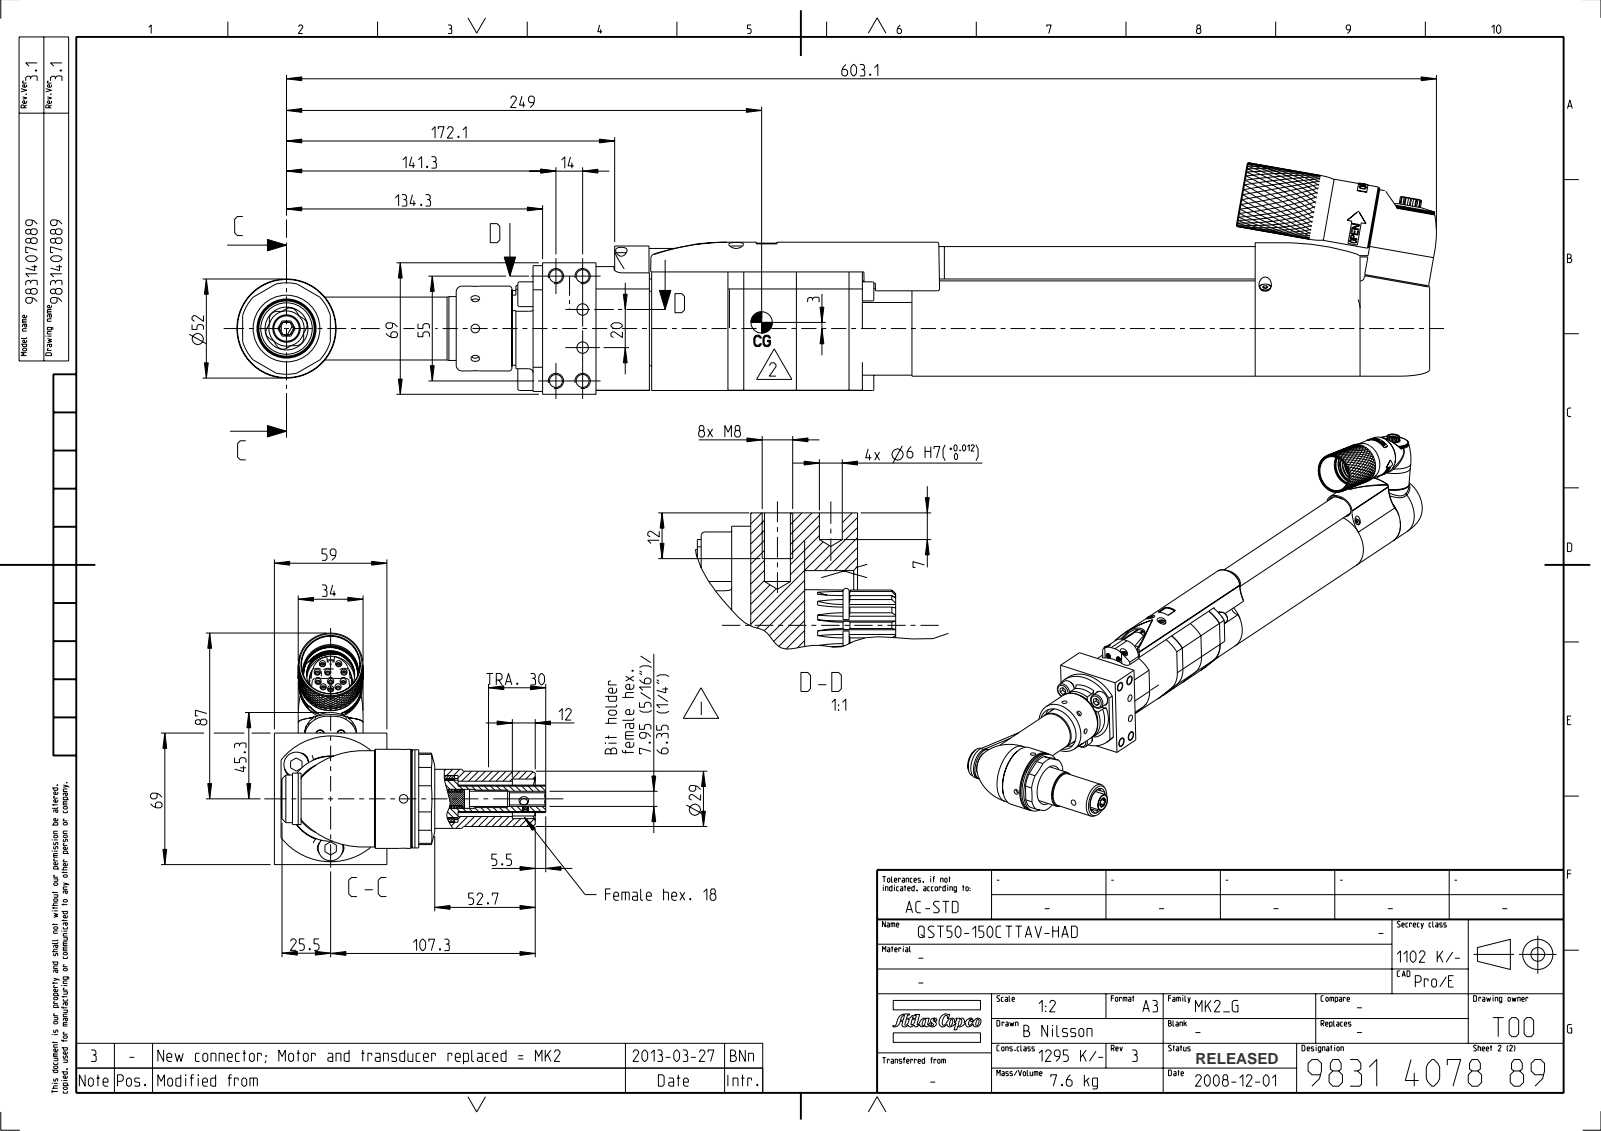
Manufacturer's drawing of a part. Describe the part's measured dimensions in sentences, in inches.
The part is named "4230260202; 4230260212_ASM; 4230265900; 0219110017 (+8 more)". Its 3-D file was written by "PRO/ENGINEER BY PARAMETRIC TECHNOLOGY CORPORATION, 2012420 (CONFIG_CONTROL_DESIGN)". It is 46 solids with 4932 faces: 1908 planar, 1658 cylindrical and 1366 other. Overall it measures 24.766 by 5.602 by 4.783 inches. Its volume is 49.96 cubic inches and its surface area 635.4 square inches. Round holes: 12 of diameter 0.177, 11 of diameter 0.104, 11 of diameter 0.129, 11 of diameter 0.142, 9 of diameter 0.13, 8 of diameter 0.315, 6 of diameter 0.128, 5 of diameter 0.268, 4 of diameter 0.076, 4 of diameter 0.194, 4 of diameter 0.236, 4 of diameter 0.354. Round bosses or shafts: 7 of diameter 0.118, 5 of diameter 0.236, 4 of diameter 0.315, 4 of diameter 0.197, 4 of diameter 0.157, 3 of diameter 1.339, 3 of diameter 0.512, 3 of diameter 0.394. Partial cylindrical surfaces (rounded edges, fillets, slot ends): 87 of radius 0.039, 53 of radius 0.004, 35 of radius 0.02, 12 of radius 0.011, 12 of radius 0.02, 11 of radius 0.079, 8 of radius 0.008, 8 of radius 0.098. The main face-to-face distances are 1.102, 1.299, 1.654, 6.524, 0.177, 2.146, 1.087, 0.374, 0.197, 2.717. The hole center spacings are 0.282, 0.292, 0.293, 0.719, 0.292, 0.768, 0.083, 0.289.
